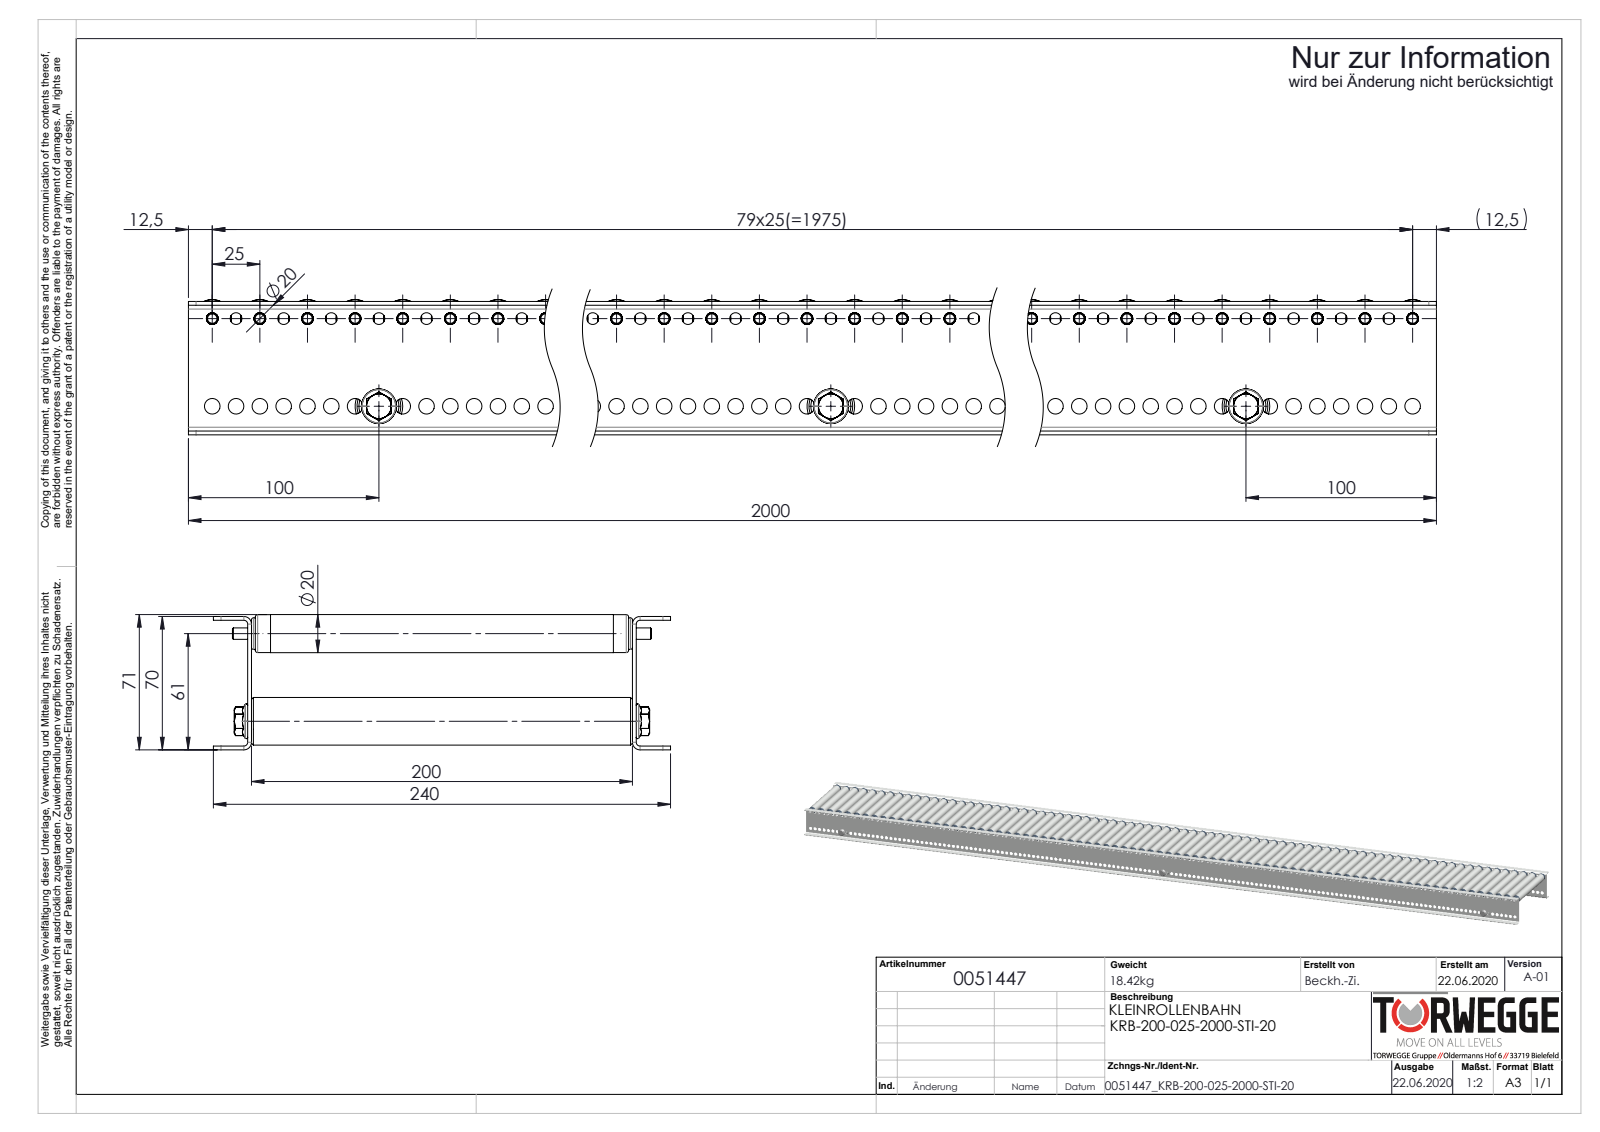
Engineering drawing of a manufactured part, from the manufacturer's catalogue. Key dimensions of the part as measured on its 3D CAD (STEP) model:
Part name (STEP PRODUCT): S100993_Tragrollenrohr-Ø20x1STI_KFG_L=180; 0051447; Profil_KRB-20x70x20x2_KFG_S100206_U-PROFIL-20-70-20-2-KRB-20-L=2000; S100992_Typ-KUT50-20x1-6 (+4 more)
STEP written by: SolidWorks 2020 (AUTOMOTIVE_DESIGN)
Units: millimetres
Bodies: 177 solids, 15746 faces (5122 planar, 5988 cylindrical, 4636 other)
Overall size (bounding box): 2000 × 240 × 71
Volume: 2 260 000 mm³ · Surface area: 3 501 000 mm²
Round holes (diameter × count): ⌀6.2 ×159, ⌀8.2 ×159, ⌀6.1 ×80, ⌀14.2 ×80, ⌀17.2 ×80, ⌀18 ×80, ⌀6.8 ×3, ⌀21 ×3
Round bosses / shafts (diameter × count): ⌀20 ×80, ⌀19.9 ×80, ⌀18.1 ×80, ⌀17.8 ×80, ⌀16.5 ×80, ⌀6 ×80, ⌀25 ×3, ⌀8 ×3
Partial cylindrical surfaces — rounded edges, fillets, slot ends (radius × count): R4.05 ×80, R4 ×8, R2 ×4
Main face-to-face distances: 2, 202, 68, 200, 204, 70, 66, 192, 18, 30
Hole centre spacings: 12.5, 25, 37.5, 50, 62.5, 75, 87.5, 100
